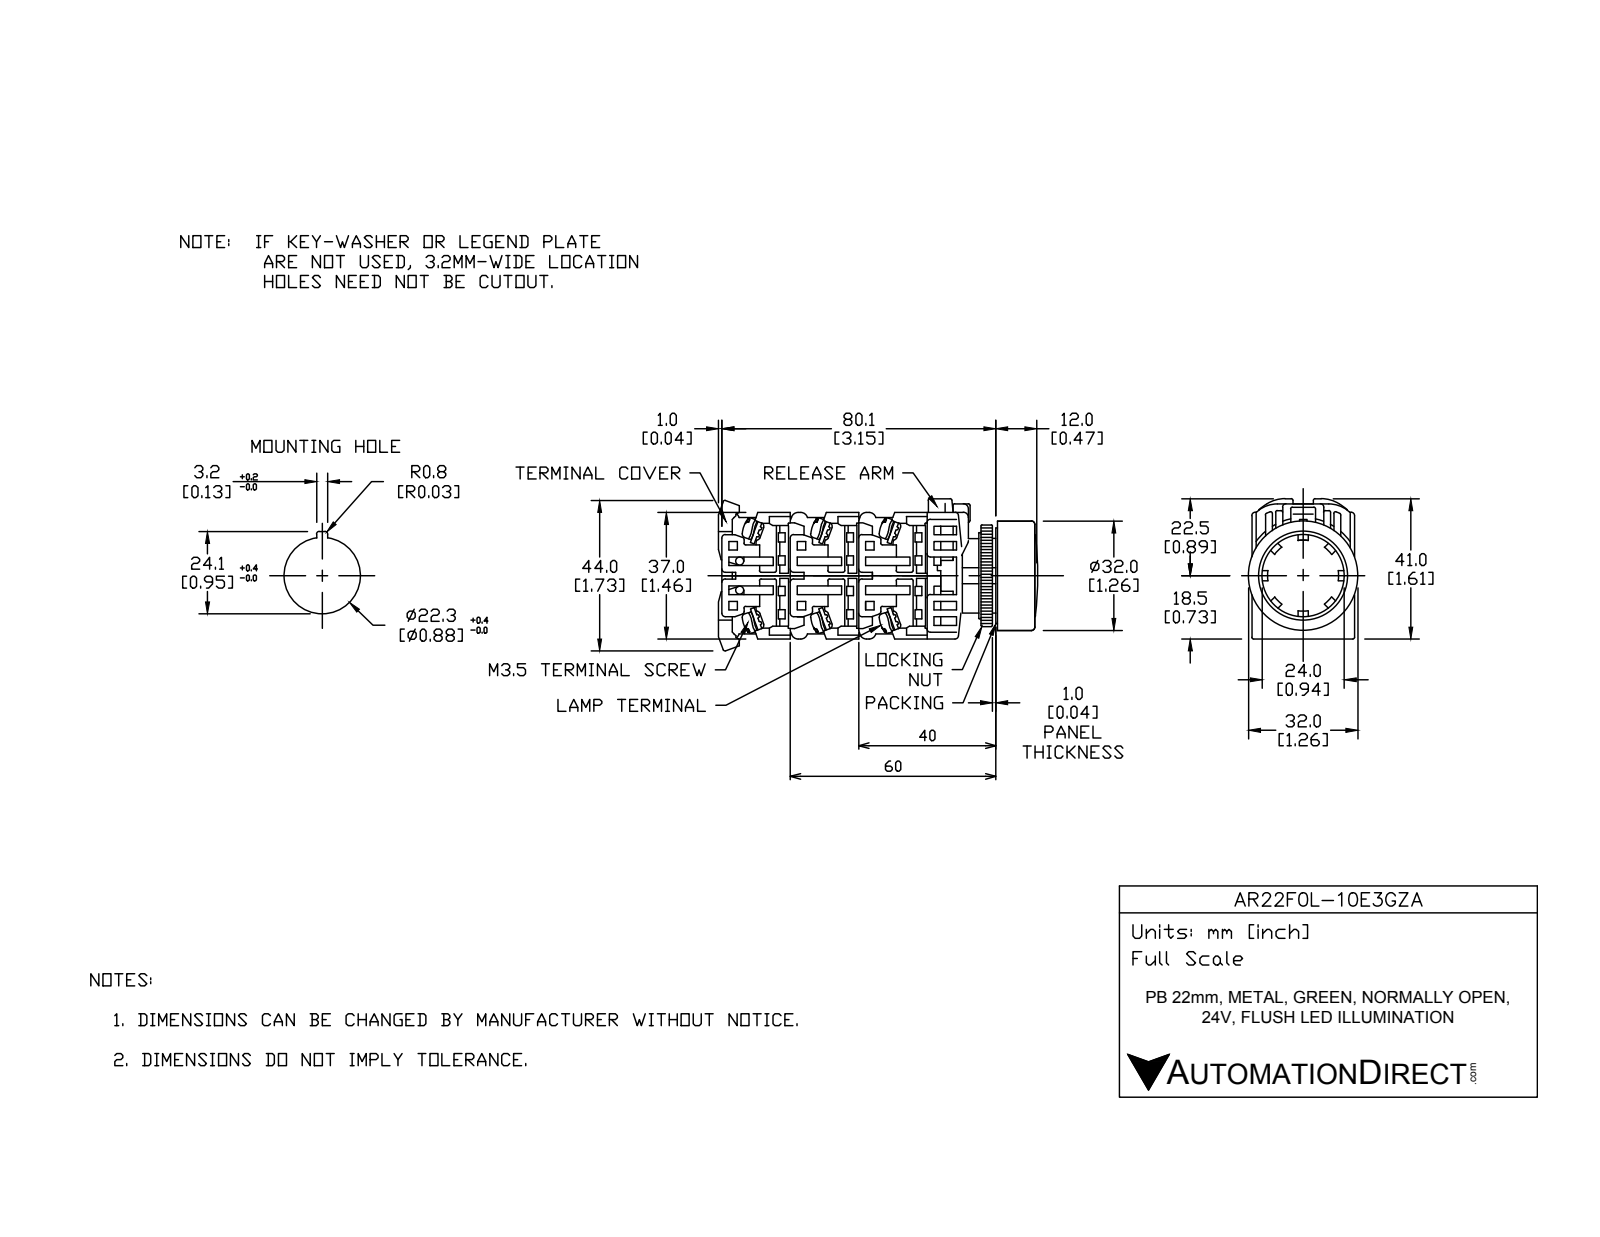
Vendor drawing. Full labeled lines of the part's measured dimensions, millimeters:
Part name (STEP PRODUCT): AR22F0L-10E3GZA
STEP written by: SolidWorks 2017 (AUTOMOTIVE_DESIGN)
Units: millimetres
Bodies: 18 solids, 475 faces (329 planar, 111 cylindrical, 35 other)
Overall size (bounding box): 52.75 × 43.81 × 32
Volume: 36 367 mm³ · Surface area: 24 064 mm²
Round holes (diameter × count): ⌀21.8 ×1, ⌀22 ×1, ⌀25 ×1, ⌀31 ×1
Round bosses / shafts (diameter × count): ⌀5 ×4, ⌀32 ×1, ⌀30.5 ×1, ⌀29.8 ×1, ⌀24 ×1, ⌀23.8 ×1, ⌀21.75 ×1, ⌀17 ×1
Partial cylindrical surfaces — rounded edges, fillets, slot ends (radius × count): R0.5 ×39, R1.75 ×8, R5 ×4, R4 ×2, R16.59 ×1, R17.59 ×1
Main face-to-face distances: 1, 18, 28.5, 48.5, 20, 29, 3, 2, 21, 0.5
